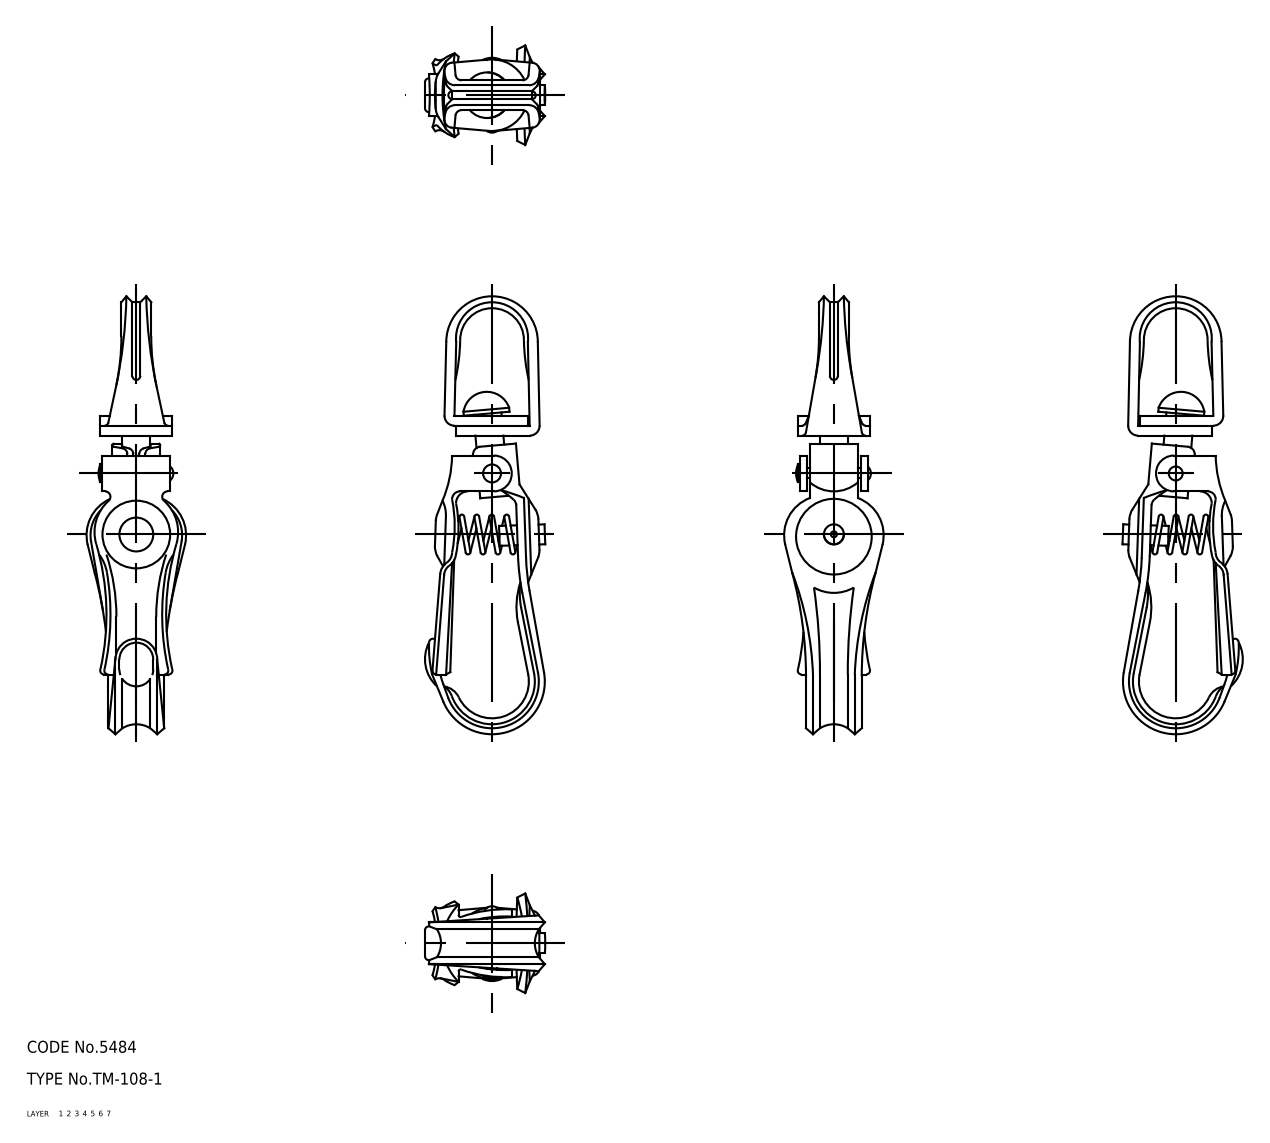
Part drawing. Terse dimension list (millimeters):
name: spring; pin_B; pin_A; stopper (+4 more)
written by: CADfix (AUTOMOTIVE_DESIGN)
unit: mm
bodies: 7 solids, 262 faces (0 planar, 0 cylindrical, 262 other)
size: 109.74 × 32.63 × 25
volume: 10 788 mm³; area: 12 214 mm²
